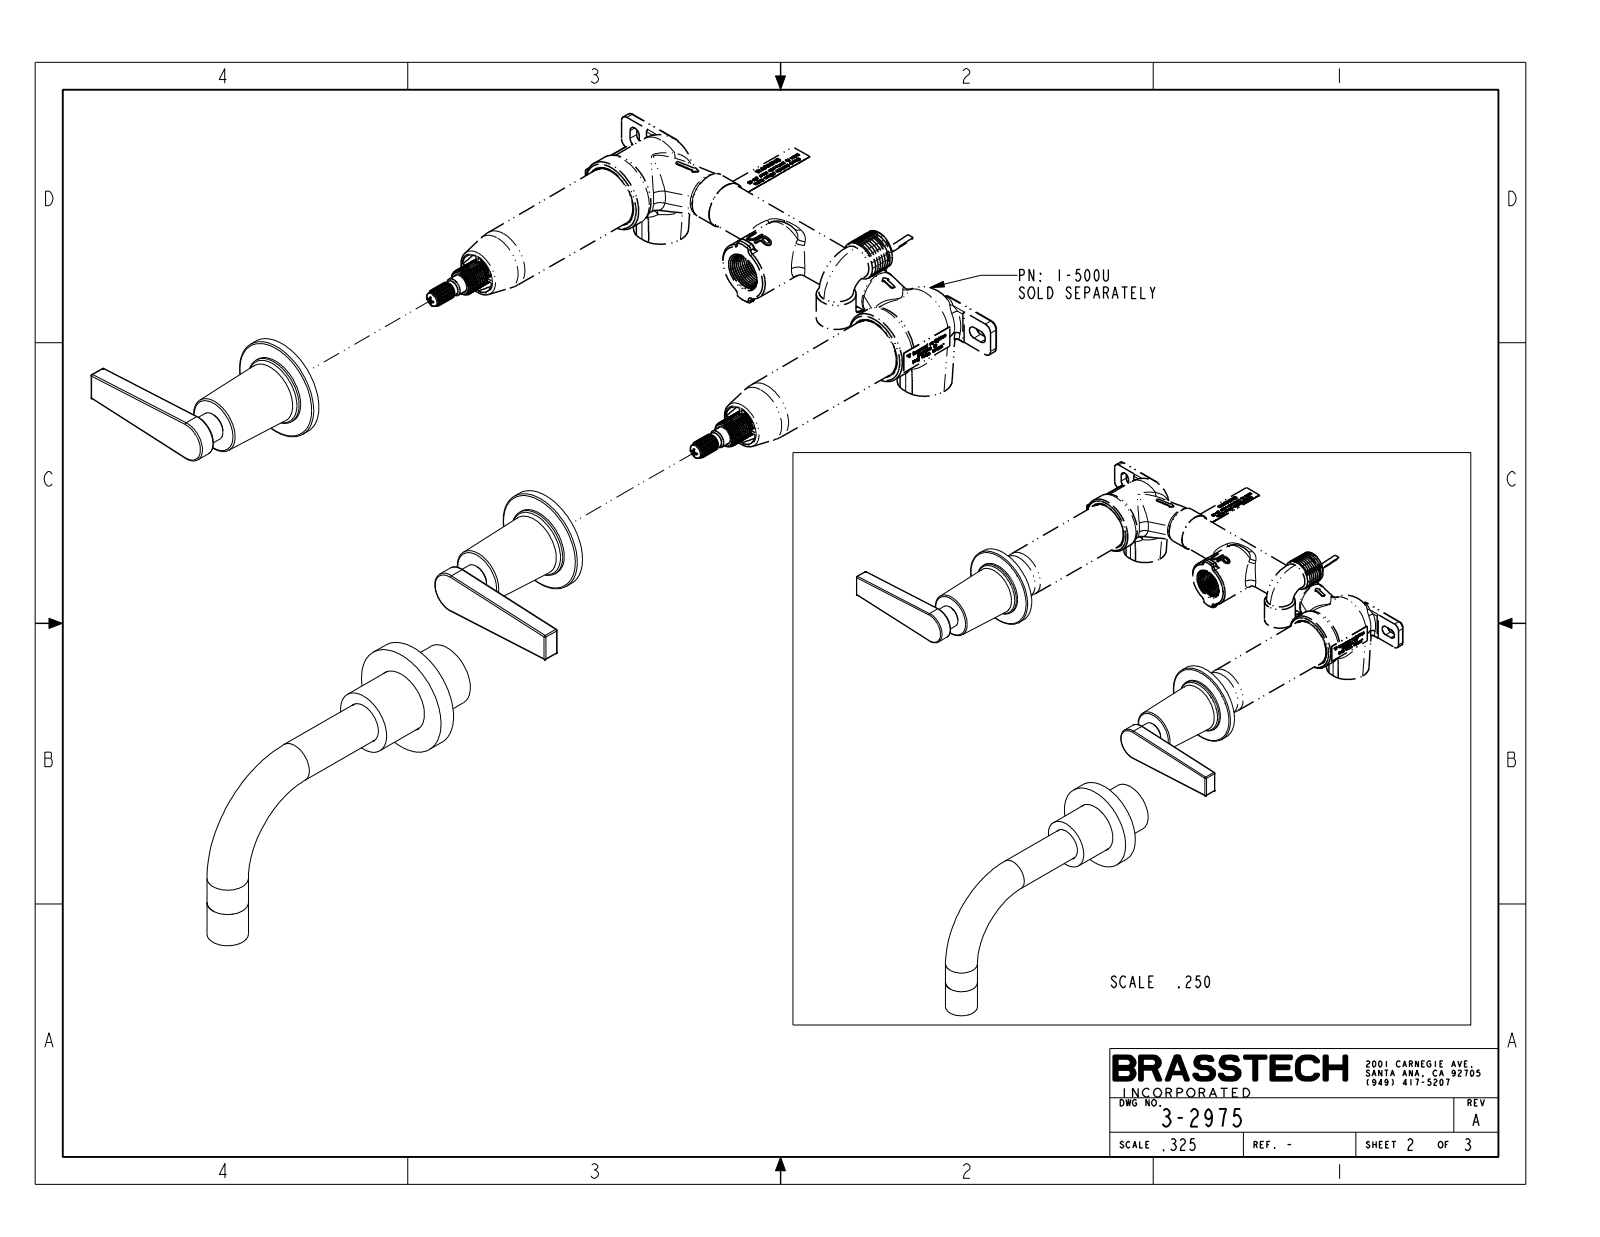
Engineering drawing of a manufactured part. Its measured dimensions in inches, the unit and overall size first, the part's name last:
Units: inches
Overall size (bounding box): 13.575 × 10.54 × 5.998
Round bosses / shafts (diameter × count): ⌀2.2 ×2, ⌀1.5 ×2, ⌀1.275 ×2, ⌀0.875 ×2, ⌀0.625 ×2, ⌀0.525 ×2, ⌀2.375 ×1, ⌀1.375 ×1
Partial cylindrical surfaces — rounded edges, fillets, slot ends (radius × count): R0.03 ×16, R0.46 ×2
Main face-to-face distances: 0.187, 2.87, 2.683, 2.495, 2.308, 0.375, 0.375, 0.188, 2.12, 2.495
Volume: 15.8 in³ · Surface area: 84.83 in²
Bodies: 3 solids, 108 faces (24 planar, 46 cylindrical, 38 other)
Part name (STEP PRODUCT): 3-2975_SW0001
STEP written by: CREO PARAMETRIC BY PTC INC, 2018400 (AUTOMOTIVE_DESIGN)
